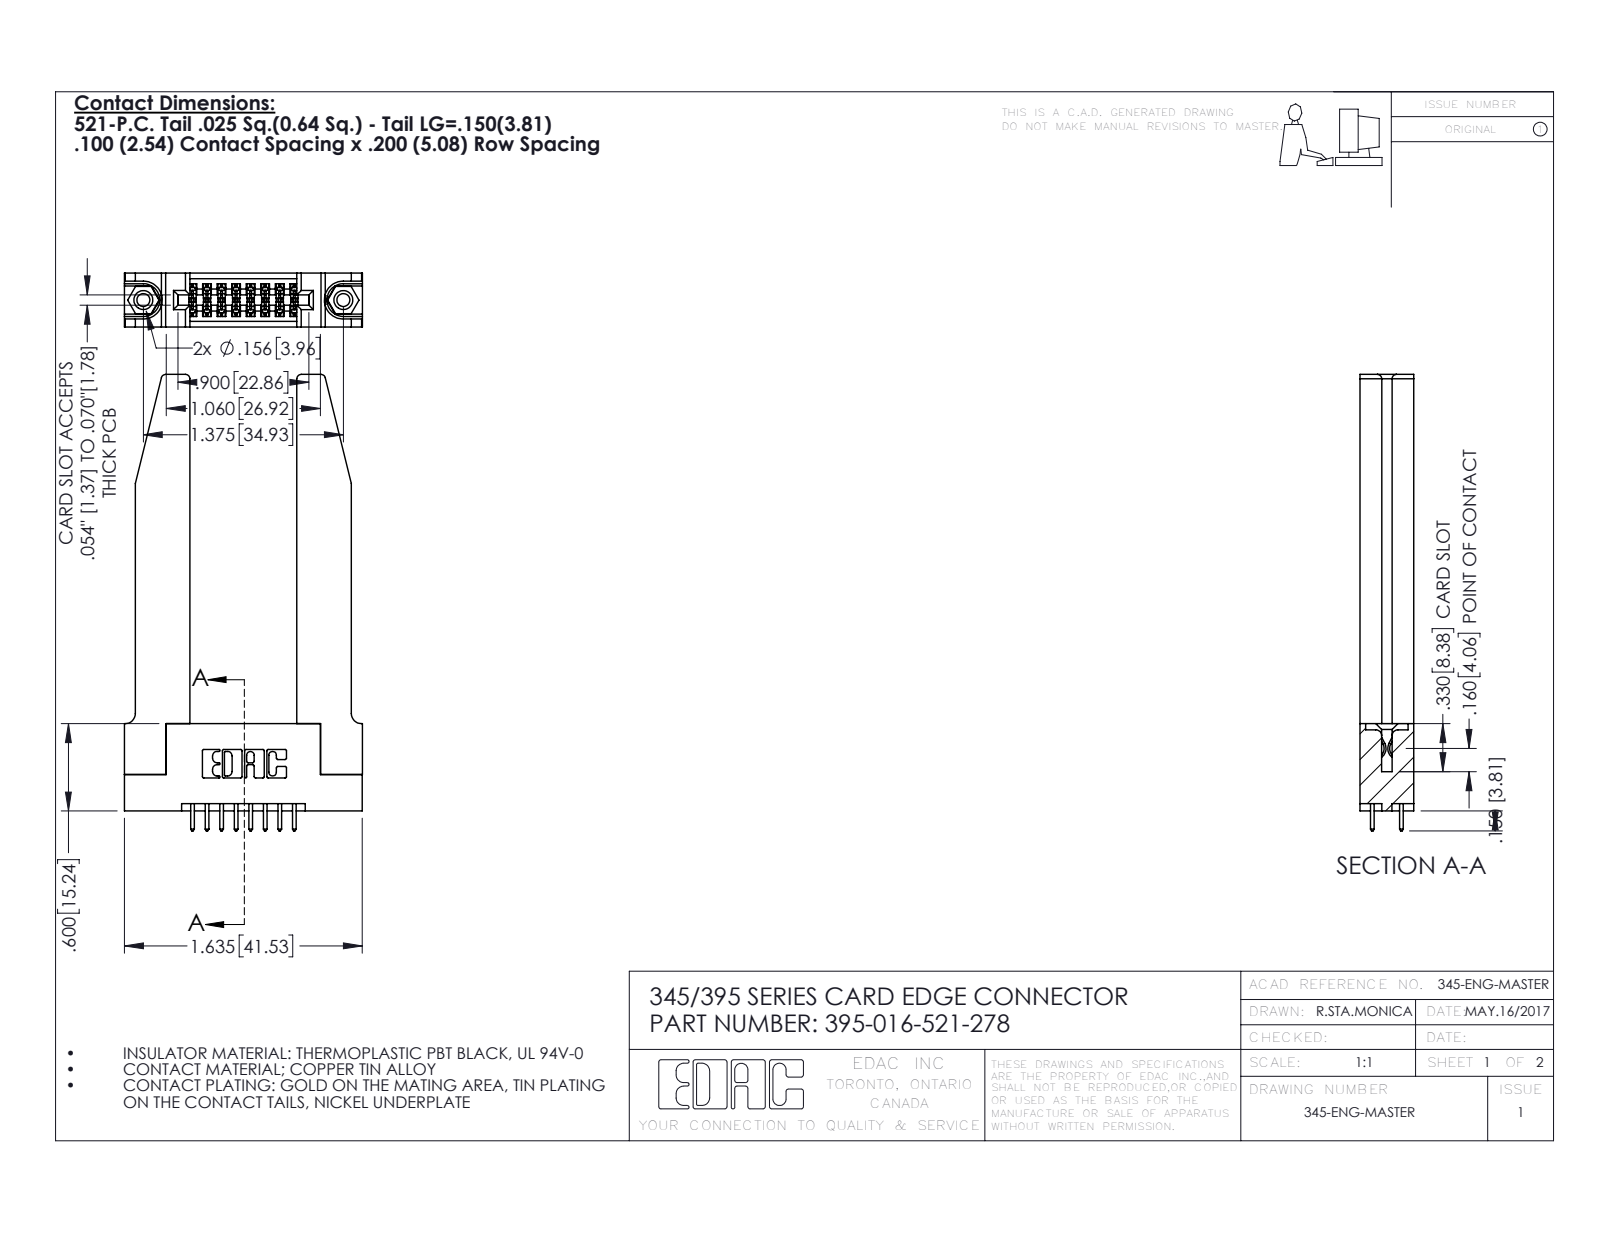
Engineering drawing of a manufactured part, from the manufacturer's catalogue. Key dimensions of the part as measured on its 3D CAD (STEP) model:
Part name (STEP PRODUCT): 345-250-001_345-250-001-102; 395-016-521-278; 345-220-078_345-220-078; 345-292-001_345-293-121 (+1 more)
STEP written by: SolidWorks 2016 (CONFIG_CONTROL_DESIGN)
Units: inches
Bodies: 21 solids, 1160 faces (750 planar, 358 cylindrical, 52 other)
Overall size (bounding box): 3.137 × 1.636 × 0.37
Volume: 0.701 in³ · Surface area: 18.02 in²
Round holes (diameter × count): ⌀0.089 ×2, ⌀0.125 ×2, ⌀0.156 ×2, ⌀0.064 ×1
Round bosses / shafts (diameter × count): ⌀0.155 ×2
Partial cylindrical surfaces — rounded edges, fillets, slot ends (radius × count): R0.006 ×24, R0.01 ×22, R0.01 ×16, R0.03 ×8, R0.007 ×6, R0.031 ×6, R0.026 ×3, R0.014 ×2
Main face-to-face distances: 0.37, 0.072, 0.298, 0.148, 0.15, 0.077, 0.22, 0.735, 0.2, 0.098
Hole centre spacings: 0.27, 1.144, 1.375
